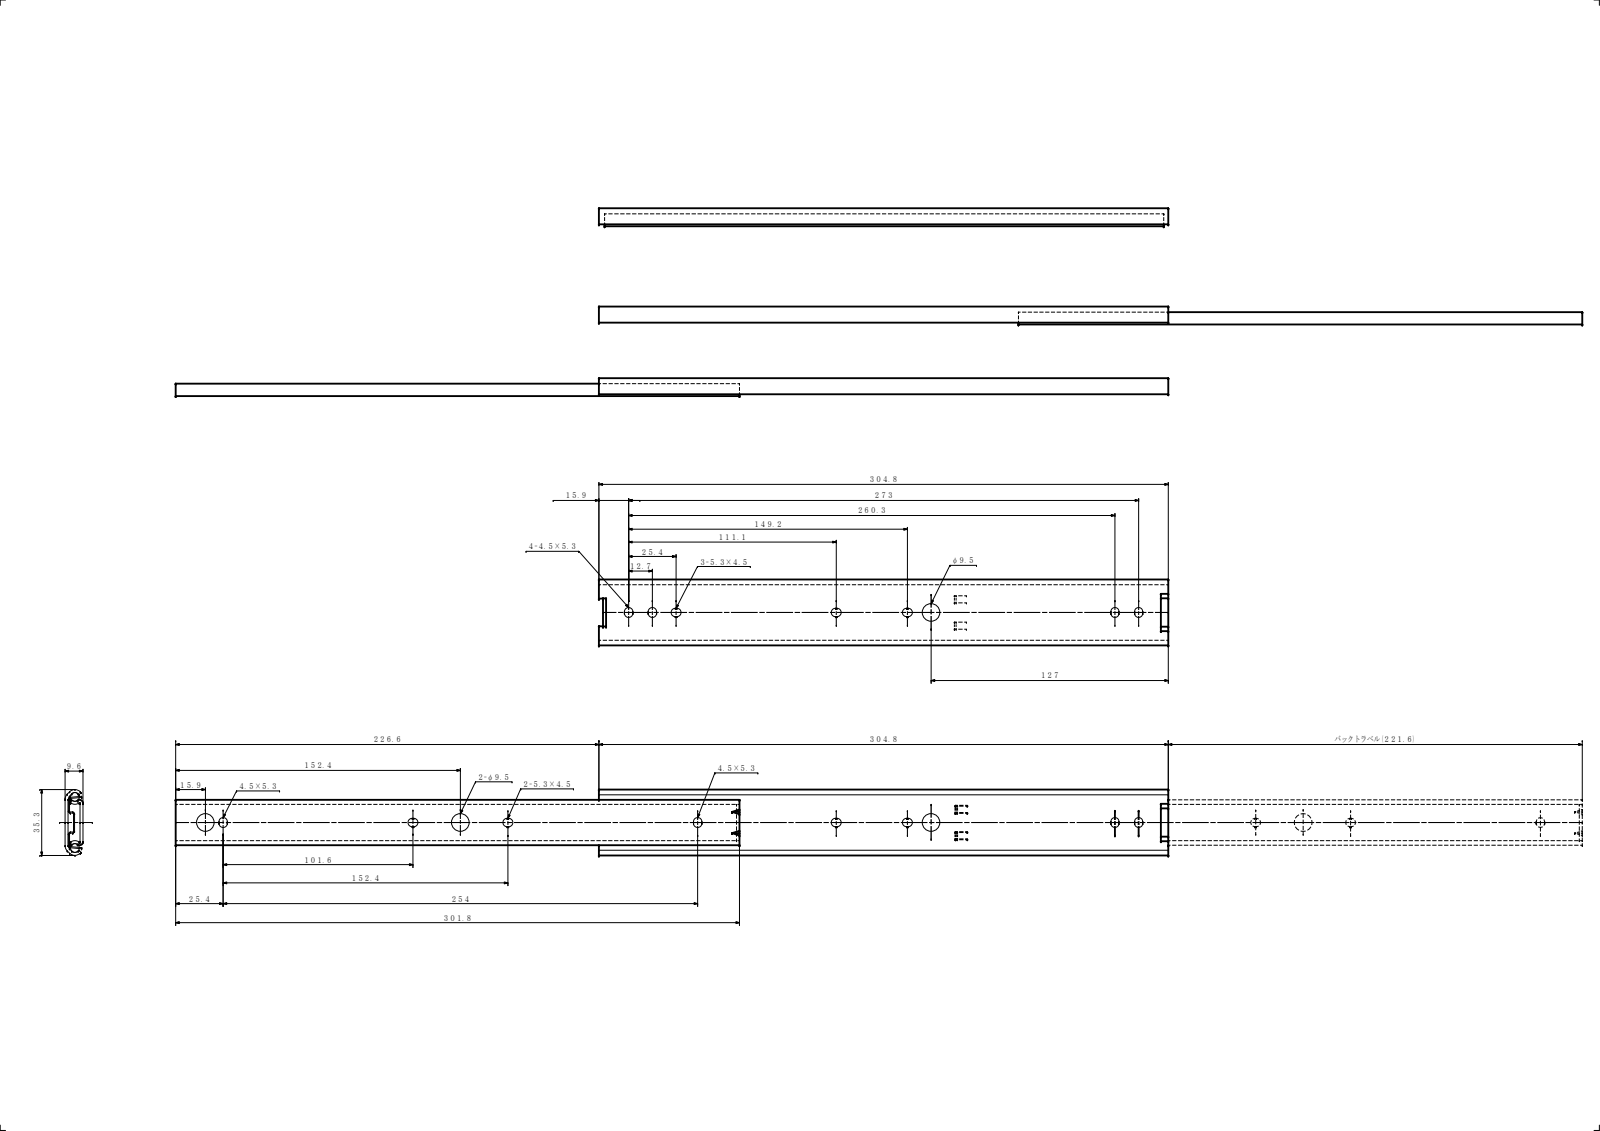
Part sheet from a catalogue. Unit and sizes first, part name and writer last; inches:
Units: inches
Overall size (bounding box): 20.919 × 1.39 × 0.378
Round holes (diameter × count): ⌀0.374 ×3
Partial cylindrical surfaces — rounded edges, fillets, slot ends (radius × count): R0.089 ×22, R0.016 ×6, R0.039 ×4, R0.098 ×4, R0.118 ×4, R0.008 ×2, R0.071 ×2, R0.079 ×2
Main face-to-face distances: 0.063, 0.315, 0.378, 0.252, 0.051, 0.264, 0.114, 0.201, 0.184, 0.121
Hole centre spacings: 5.374, 9.919, 15.293
Volume: 2.31 in³ · Surface area: 77.48 in²
Bodies: 2 solids, 138 faces (68 planar, 70 cylindrical, 0 other)
Part name (STEP PRODUCT): OM 3520-12; 3520-12; IM 3520-12
STEP written by: SolidWorks 2019 (CONFIG_CONTROL_DESIGN)
